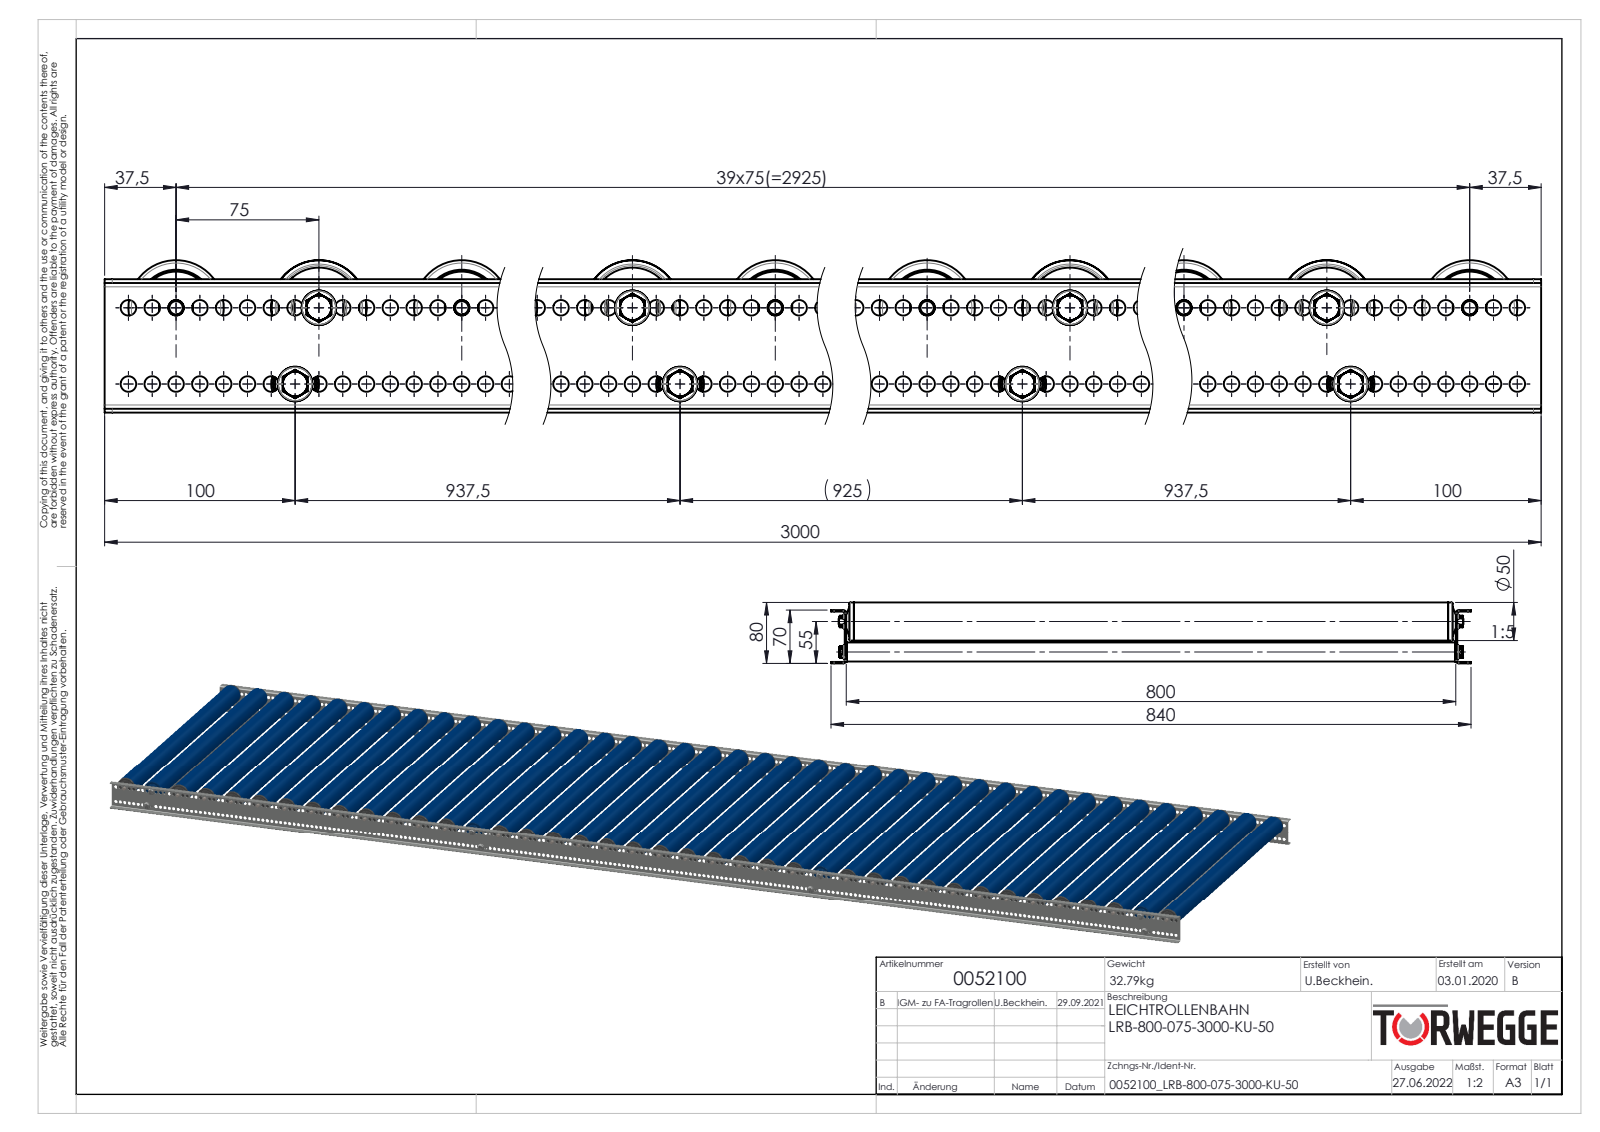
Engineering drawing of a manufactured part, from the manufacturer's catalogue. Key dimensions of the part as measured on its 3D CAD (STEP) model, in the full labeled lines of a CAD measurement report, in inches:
Part name (STEP PRODUCT): Druckfeder_1,2x10x30; S100994_Sperrzahnschraube_M08x16-8.8-A2K; 0039778-Achse-ST-Ø08-KFG_AL820-G; KUT100-50x2,8-KB-A8-FA_KFG_0054463_KUT100-50x2,8-KB-A8-FA-EL=800 (+8 more)
STEP written by: SolidWorks 2020 (AUTOMOTIVE_DESIGN)
Units: inches
Bodies: 634 solids, 12220 faces (3052 planar, 5720 cylindrical, 3448 other)
Overall size (bounding box): 118.11 × 33.071 × 3.15
Volume: 1 137 in³ · Surface area: 20 960 in²
Round holes (diameter × count): ⌀0.323 ×478, ⌀0.299 ×36, ⌀0.315 ×36, ⌀0.984 ×36, ⌀1.181 ×36, ⌀1.378 ×36, ⌀1.551 ×36, ⌀1.575 ×36, ⌀0.268 ×8, ⌀0.472 ×4, ⌀0.476 ×4, ⌀0.63 ×4
Round bosses / shafts (diameter × count): ⌀1.969 ×40, ⌀1.748 ×36, ⌀1.496 ×36, ⌀1.417 ×36, ⌀1.299 ×36, ⌀0.866 ×36, ⌀0.827 ×36, ⌀0.984 ×8
Partial cylindrical surfaces — rounded edges, fillets, slot ends (radius × count): R0.024 ×72, R0.03 ×72, R0.096 ×72, R0.192 ×36, R0.276 ×36, R0.157 ×8, R0.079 ×4, R0.098 ×4
Main face-to-face distances: 0.079, 31.575, 2.677, 31.496, 31.654, 2.756, 2.598, 31.181, 0.472, 0.236
Hole centre spacings: 0.492, 0.984, 1.476, 1.969, 2.461, 2.953, 3.445, 3.937
